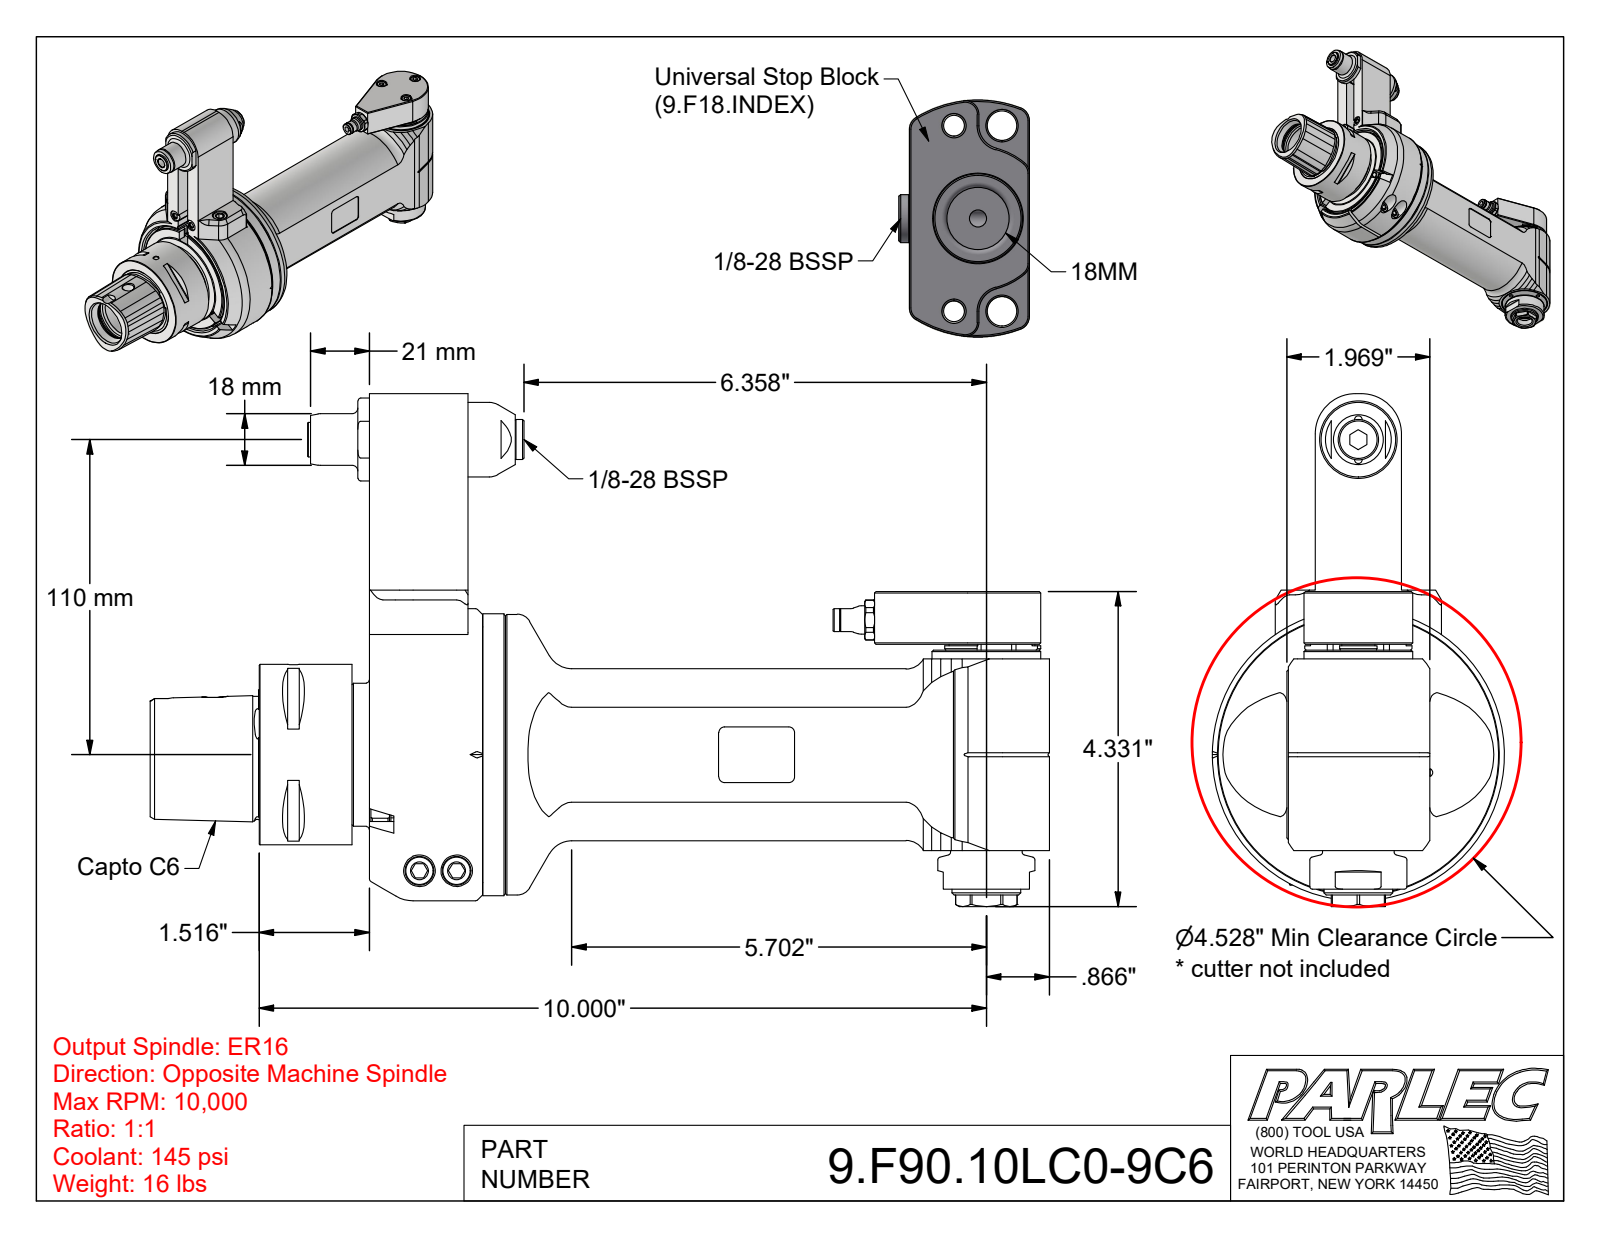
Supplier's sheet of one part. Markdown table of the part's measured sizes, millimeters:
| quantity | value |
| --- | --- |
| part name | 9.F90.10LC0-9C6; 9GA11C_661 (Type 1, Capto C6, 110mm); 9_F90_10LB0 |
| STEP written by | Autodesk Inventor 2022 (AUTOMOTIVE_DESIGN) |
| units | millimeters |
| bodies | 3 solids, 834 faces (349 planar, 214 cylindrical, 271 other) |
| overall size | 314 × 179 × 102 |
| volume | 1 166 000 mm³ |
| surface area | 174 900 mm² |
| round holes (diameter × count) | 8.5 × 20, 1.6 × 4, 3.2 × 4, 4.2 × 4, 6.5 × 3, 7.5 × 3, 11 × 3, 13 × 3, 2.6 × 2, 3.3 × 2, 4 × 2, 5 × 2 |
| round bosses / shafts (diameter × count) | 10 × 4, 7 × 4, 12 × 2, 8 × 2, 6 × 2, 2.5 × 2, 102 × 1, 98.4 × 1 |
| partial cylindrical surfaces (radius × count) | 1 × 14, 2 × 12, 3 × 6, 4 × 4, 0.4 × 2, 0.5 × 2, 8 × 2, 14 × 2 |
| main face-to-face distances | 10, 50, 8.5, 40, 0.5, 39.5, 32, 13.5, 7, 7.5 |
| hole center spacings | 38.5, 54.5, 46.3, 76.3, 67.3, 14.1, 21.2, 40.8 |
